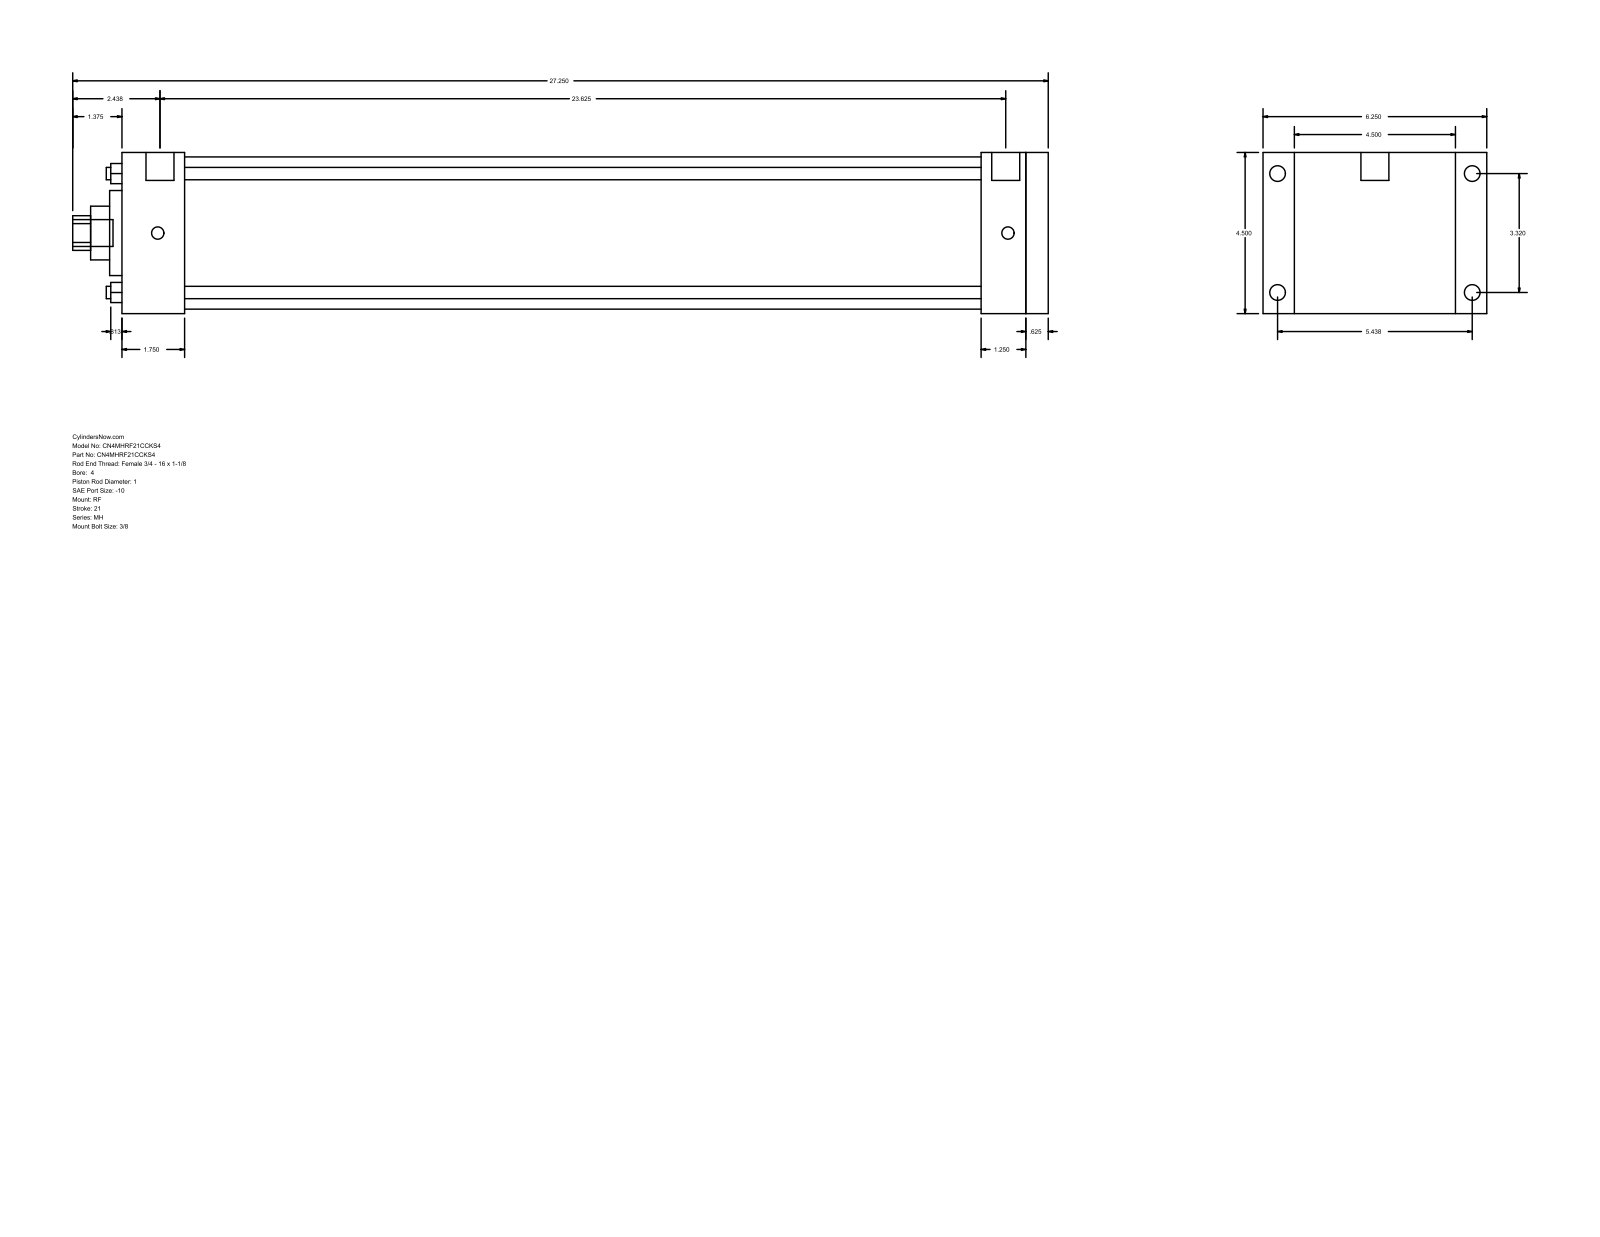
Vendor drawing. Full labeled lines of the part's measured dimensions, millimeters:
Part name (STEP PRODUCT): MH_RF__0400_1
STEP written by: GSSL Pune (CONFIG_CONTROL_DESIGN)
Units: millimetres
Bodies: 0 solids, 94 faces (65 planar, 29 cylindrical, 0 other)
Overall size (bounding box): 692.15 × 158.75 × 114.3
Round holes (diameter × count): ⌀8.76 ×4, ⌀25.4 ×1, ⌀38.1 ×1, ⌀60.33 ×1, ⌀107.95 ×1
Round bosses / shafts (diameter × count): ⌀11.13 ×4, ⌀8.73 ×4, ⌀19.84 ×2, ⌀19.05 ×1
Partial cylindrical surfaces — rounded edges, fillets, slot ends (radius × count): R12.29 ×1
Main face-to-face distances: 114.3, 657.23, 641.35, 15.88, 47.63, 44.46, 596.89, 612.77, 609.6, 565.14
Hole centre spacings: 59.62, 84.32, 119.25
